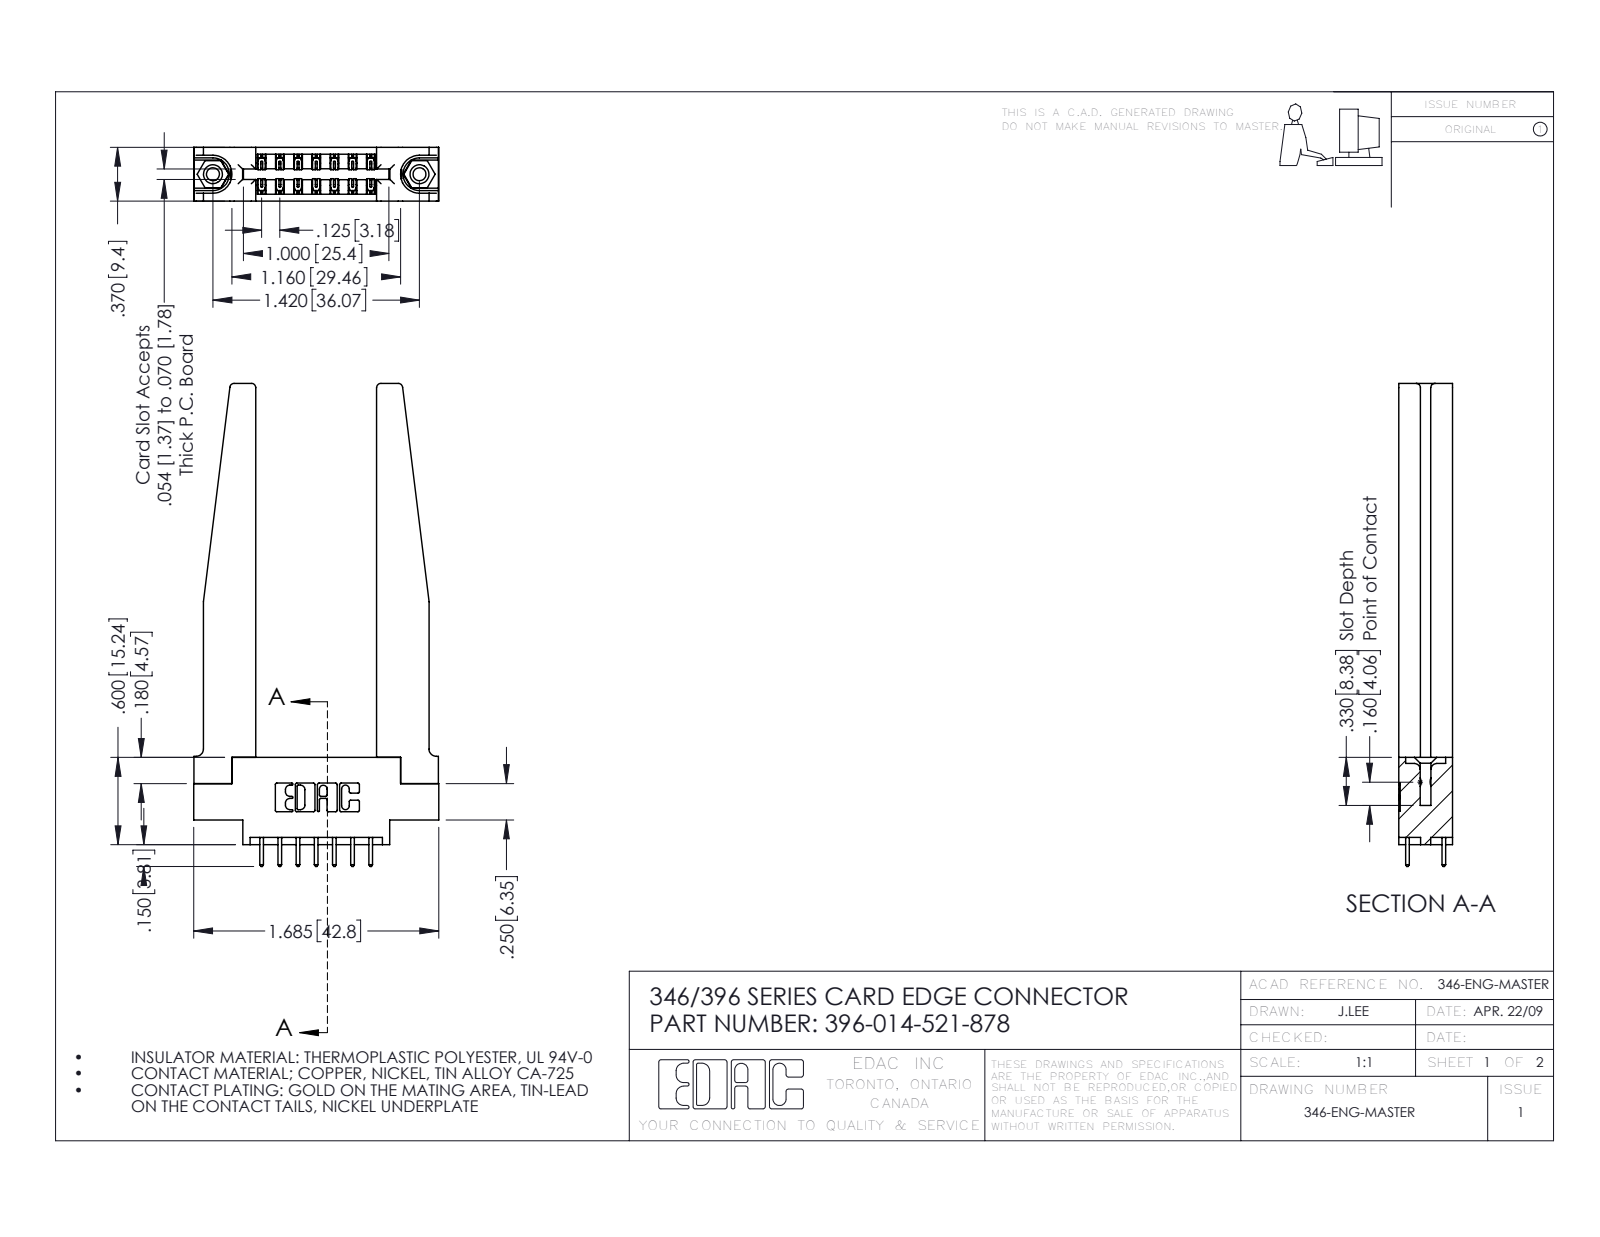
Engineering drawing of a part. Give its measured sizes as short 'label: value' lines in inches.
name: 346 Part_0.170 Offset - 0.156 Dia-TH; 345-250-001_345-250-001-102; 345-292-001_345-293-121; 396-014-521-878 (+1 more)
written by: SolidWorks 2016 (CONFIG_CONTROL_DESIGN)
unit: in
bodies: 19 solids, 1088 faces (712 planar, 324 cylindrical, 52 other)
size: 3.32 × 1.685 × 0.37
volume: 0.65 in³; area: 17.47 in²
holes: 2× ⌀0.089, 2× ⌀0.125, 2× ⌀0.156, 1× ⌀0.064
bosses: 2× ⌀0.155
rounds: 22× R0.01, 21× R0.006, 14× R0.01, 8× R0.03, 6× R0.007, 6× R0.031, 3× R0.026, 2× R0.014
face distances: 0.37, 0.15, 0.22, 0.25, 0.072, 0.148, 0.831, 0.102, 0.048, 0.322
hole spacings: 0.246, 1.217, 1.42
